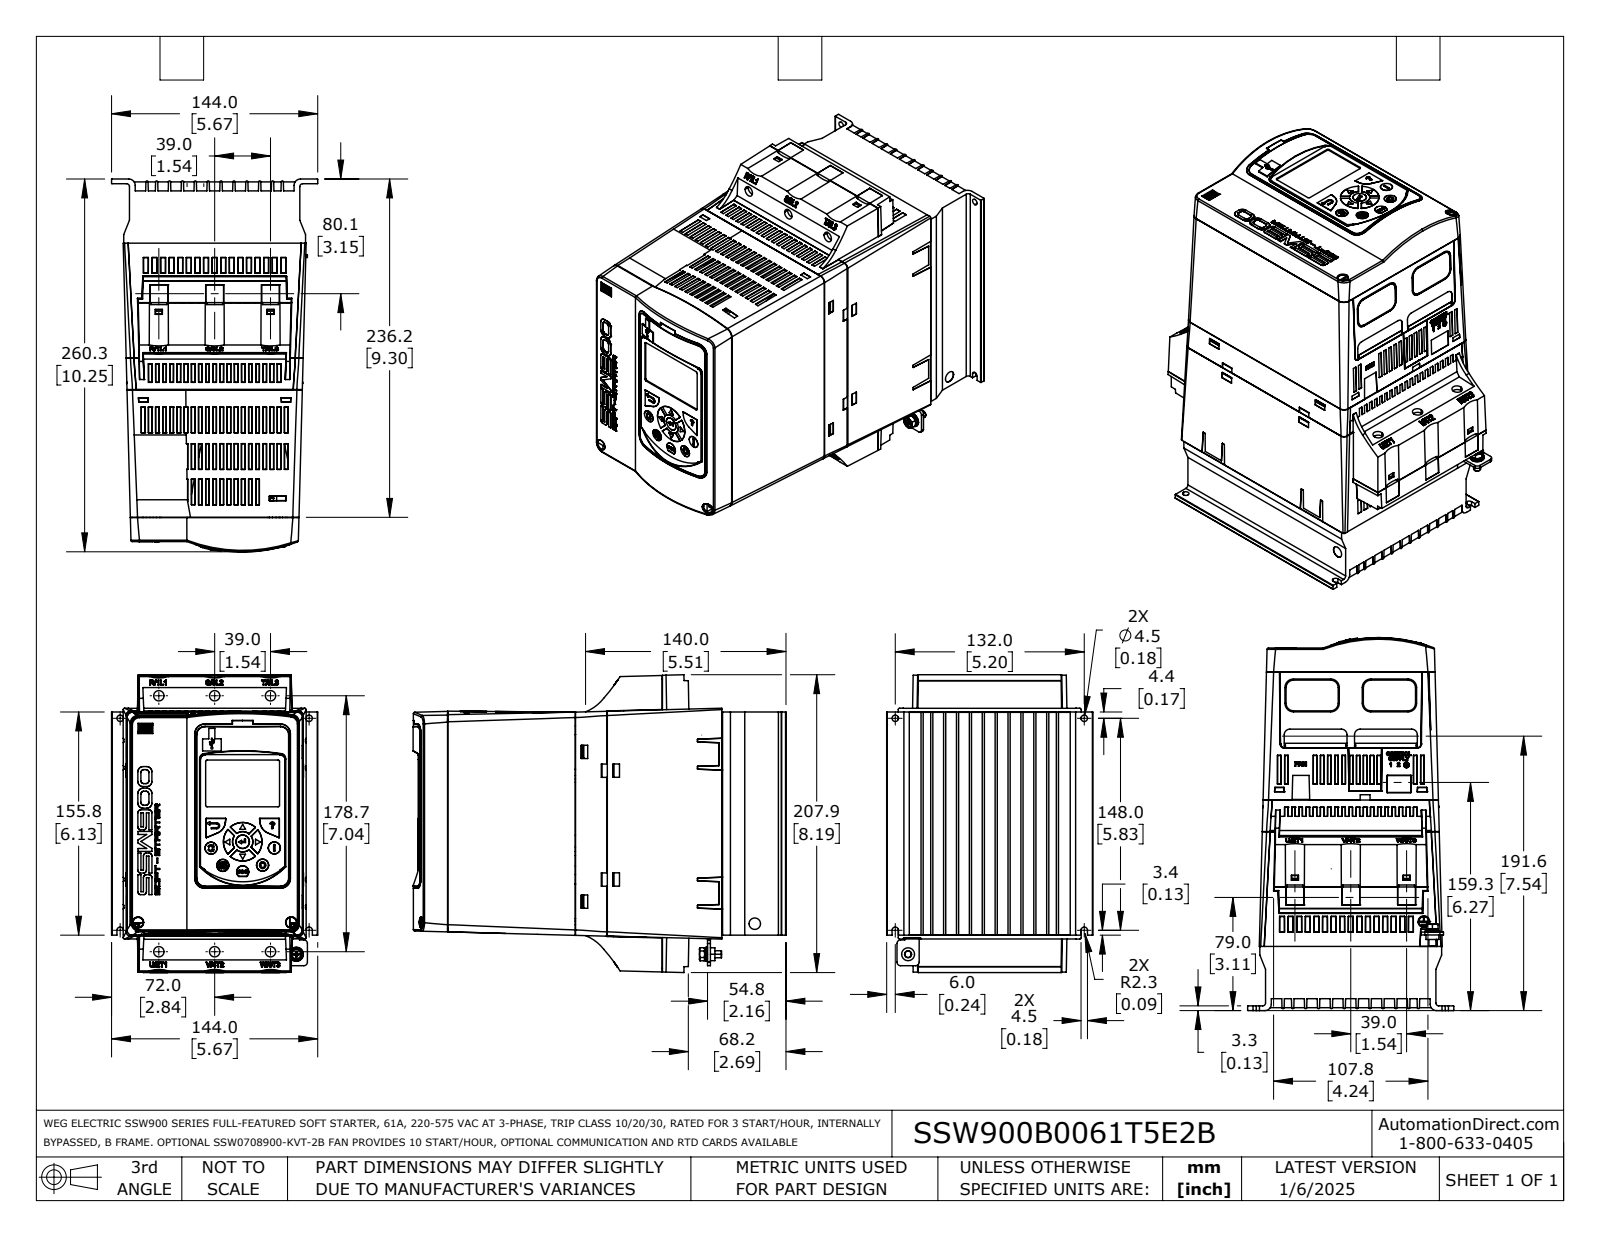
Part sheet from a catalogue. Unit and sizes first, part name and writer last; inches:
Units: inches
Overall size (bounding box): 10.254 × 8.187 × 5.669
Round holes (diameter × count): ⌀0.283 ×6, ⌀0.177 ×2, ⌀0.118 ×1, ⌀0.133 ×1, ⌀0.165 ×1, ⌀0.248 ×1, ⌀0.277 ×1, ⌀0.285 ×1, ⌀0.315 ×1
Round bosses / shafts (diameter × count): ⌀0.387 ×1, ⌀0.354 ×1, ⌀0.323 ×1, ⌀0.317 ×1, ⌀0.264 ×1, ⌀0.197 ×1, ⌀0.193 ×1, ⌀0.151 ×1
Partial cylindrical surfaces — rounded edges, fillets, slot ends (radius × count): R0.012 ×28, R0.008 ×16, R0.03 ×12, R0.02 ×9, R0.006 ×7, R0.017 ×4, R0.039 ×4, R0.098 ×4
Main face-to-face distances: 5.707, 5.715, 9.887, 4.179, 4.171, 0.098, 6.134, 7.007, 0.7, 0.783
Hole centre spacings: 1.535, 7.201, 7.035, 3.071, 7.676, 0.713, 0.886, 0.985
Volume: 310.3 in³ · Surface area: 437 in²
Bodies: 6 solids, 3794 faces (2929 planar, 209 cylindrical, 656 other)
Part name (STEP PRODUCT): SSW900B0061T5E2B
STEP written by: SolidWorks 2021 (AUTOMOTIVE_DESIGN)
